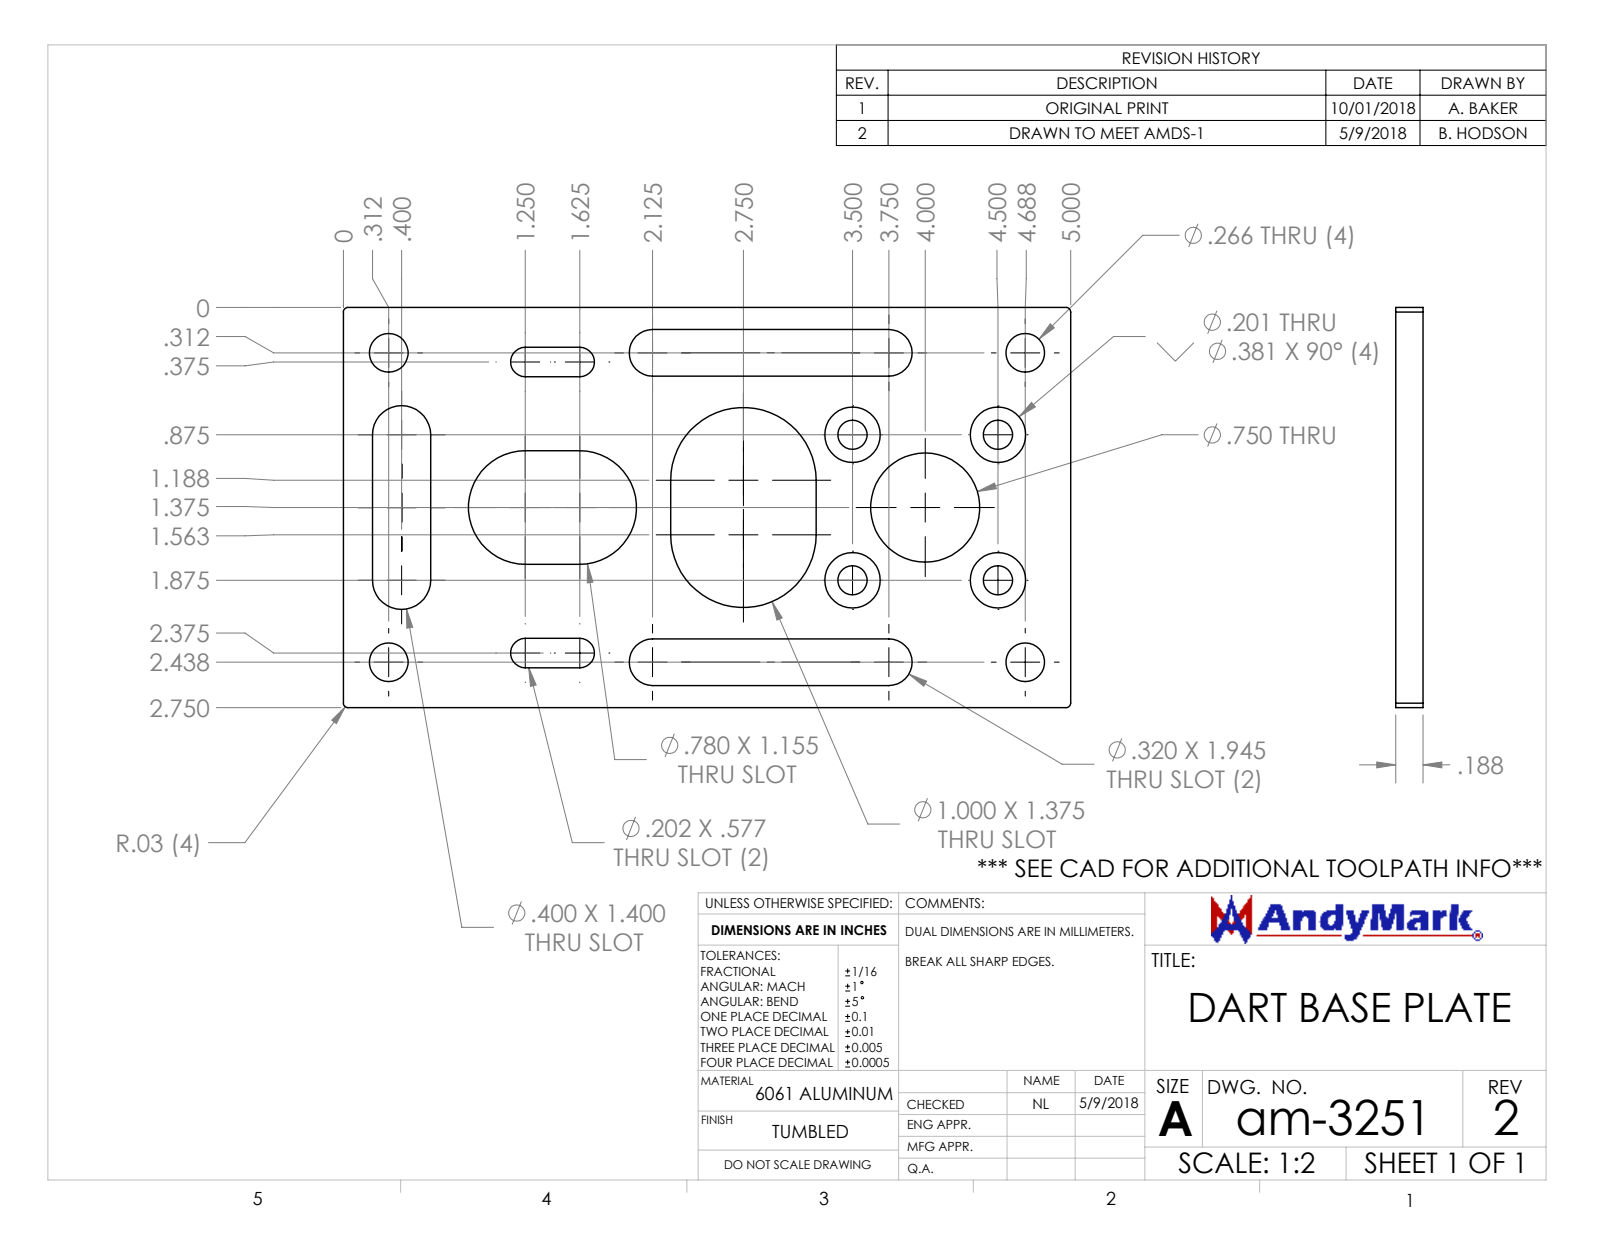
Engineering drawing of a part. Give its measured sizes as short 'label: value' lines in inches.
name: am-3251 DART Base Plate REV2
written by: SolidWorks 2017 (CONFIG_CONTROL_DESIGN)
unit: in
bodies: 1 solid, 66 faces (20 planar, 38 cylindrical, 8 other)
size: 5 × 2.75 × 0.188
volume: 1.69 in³; area: 26.57 in²
holes: 4× ⌀0.201, 4× ⌀0.266, 1× ⌀0.75
rounds: 4× R0.031, 4× R0.101, 4× R0.16, 2× R0.2, 2× R0.39, 2× R0.5
face distances: 0.187, 2.75, 0.152, 0.472, 2.278, 2.598, 0.32, 2.126, 5, 2.446
hole spacings: 0.707, 1, 0.594, 1.315, 1.574, 2.126, 3.237, 3.551
